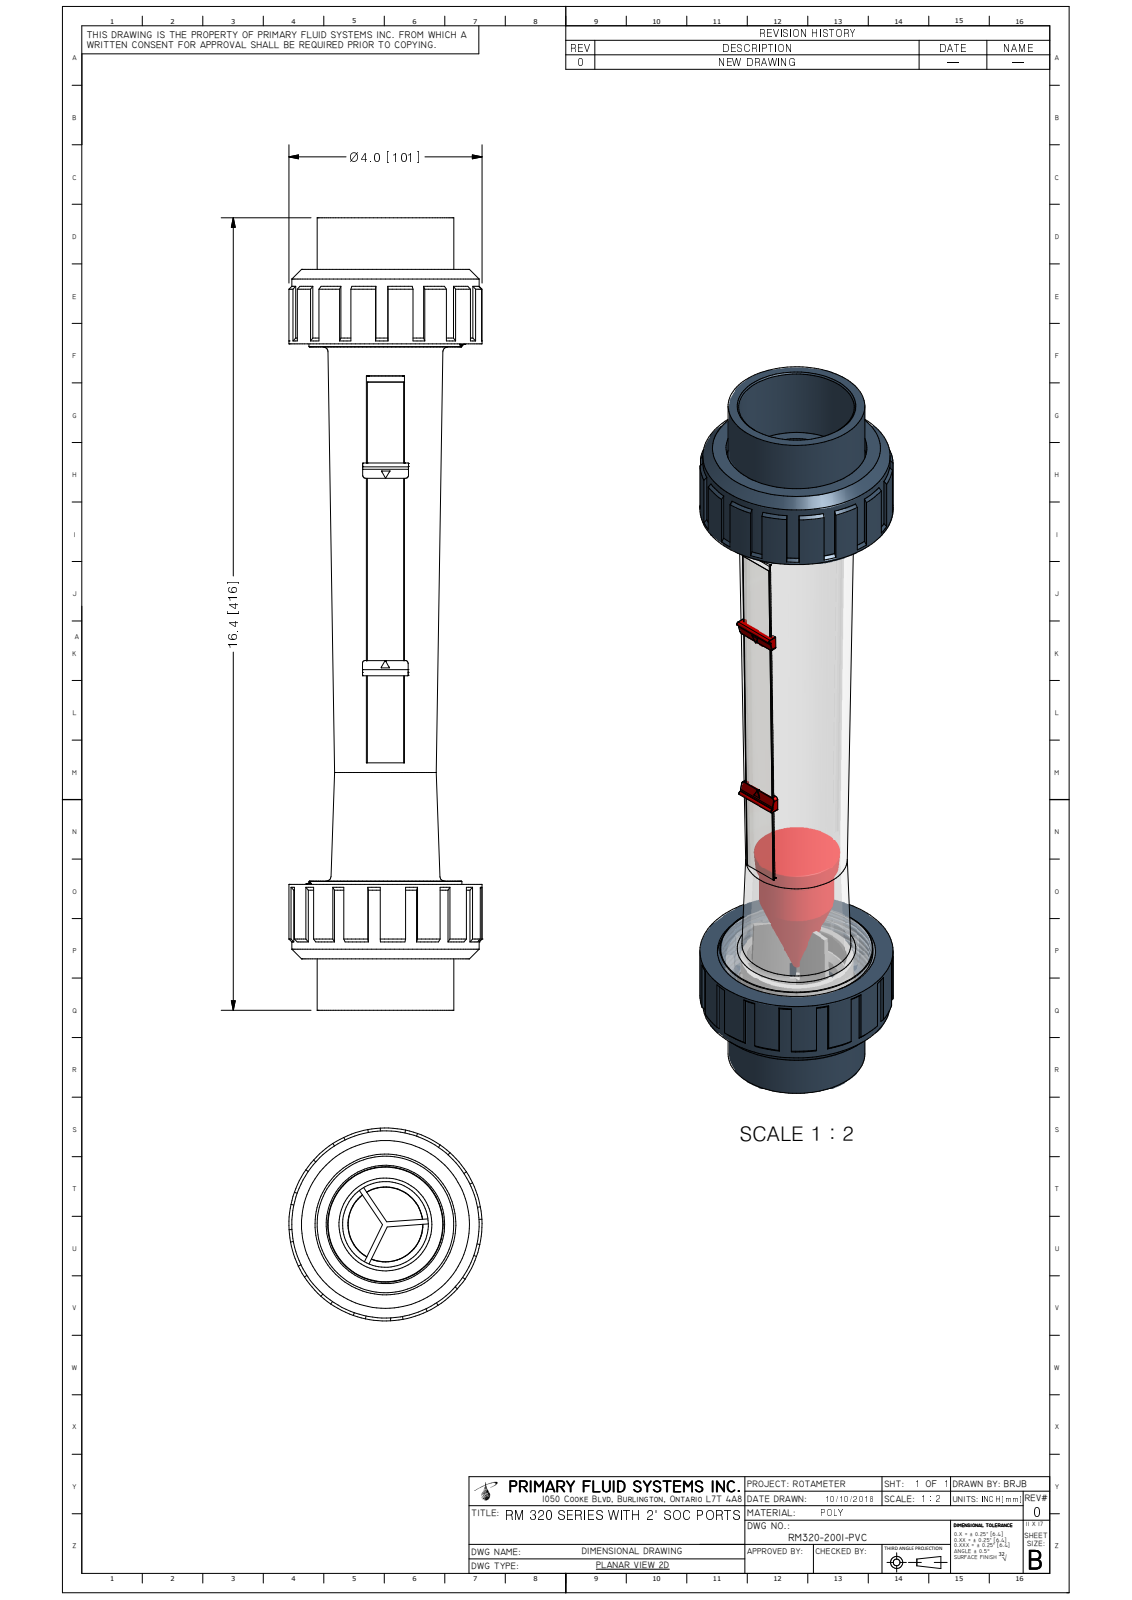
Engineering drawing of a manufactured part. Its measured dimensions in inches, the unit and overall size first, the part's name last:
Units: inches
Overall size (bounding box): 16.388 × 3.99 × 3.99
Round holes (diameter × count): ⌀2.91 ×1, ⌀3.147 ×1, ⌀3.265 ×1, ⌀3.265 ×1
Round bosses / shafts (diameter × count): ⌀3.99 ×1, ⌀3.87 ×1, ⌀3.158 ×1, ⌀3.062 ×1, ⌀2.824 ×1
Partial cylindrical surfaces — rounded edges, fillets, slot ends (radius × count): R0.008 ×18, R0.01 ×16, R0.004 ×8, R0.006 ×8, R0.06 ×4, R0.008 ×2, R0.04 ×2, R0.75 ×2
Main face-to-face distances: 1.105, 12.283, 0.435, 1.54, 12.718, 13.823, 1.174, 12.214, 0.069, 11.109
Volume: 78.51 in³ · Surface area: 285.5 in²
Bodies: 1 solid, 551 faces (187 planar, 108 cylindrical, 256 other)
Part name (STEP PRODUCT): RM320-200I-PVC_R0
STEP written by: Autodesk Inventor 2009 (AUTOMOTIVE_DESIGN)
